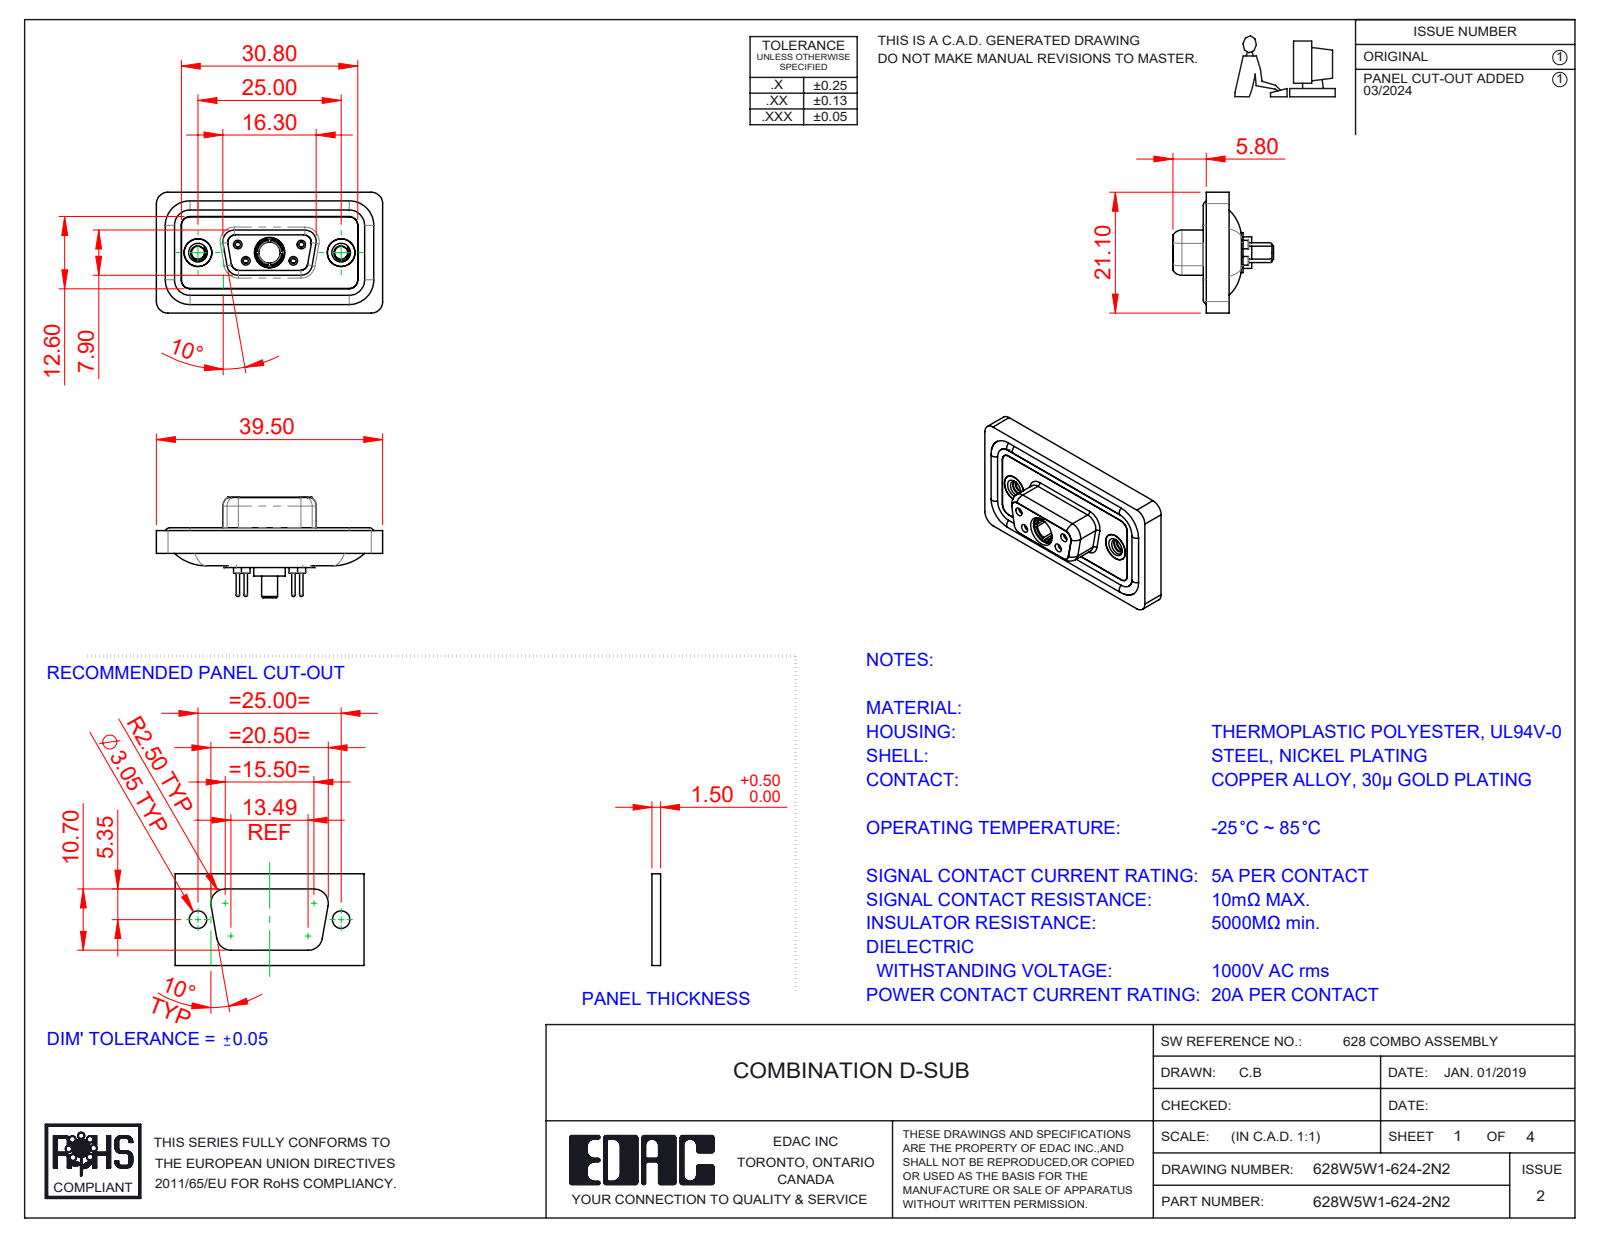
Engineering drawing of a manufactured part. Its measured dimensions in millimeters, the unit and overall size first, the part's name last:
Units: millimetres
Overall size (bounding box): 39.5 × 21.1 × 17.55
Round holes (diameter × count): ⌀0.9 ×4, ⌀1.1 ×4, ⌀1.5 ×4, ⌀2 ×4, ⌀4.85 ×3, ⌀1.6 ×2, ⌀1.7 ×2, ⌀2.26 ×2, ⌀4 ×2, ⌀4.05 ×2, ⌀5 ×2, ⌀3.7 ×1
Round bosses / shafts (diameter × count): ⌀1.6 ×6, ⌀2.2 ×4, ⌀0.6 ×4, ⌀4.95 ×2, ⌀4.8 ×2, ⌀5.5 ×1, ⌀5.2 ×1, ⌀4.96 ×1
Partial cylindrical surfaces — rounded edges, fillets, slot ends (radius × count): R1.5 ×22, R2 ×18, R1.35 ×8, R1.6 ×8, R0.25 ×4, R0.5 ×4, R0.6 ×4, R0.65 ×4
Main face-to-face distances: 0.4, 2.9, 1.1, 1.8, 1.6, 0.5, 5.65, 7.45, 5.35, 6.6
Hole centre spacings: 3.16, 5.72, 7.1, 12.5, 18.1, 4.39, 4.4, 8.31
Volume: 4 767 mm³ · Surface area: 7 635 mm²
Bodies: 13 solids, 680 faces (194 planar, 287 cylindrical, 199 other)
Part name (STEP PRODUCT): 628W5W1-624-2N2; 628Combo Shell Rear_09 Contacts; 628Combo Contact Row 1_24; 628Combo Shell Front_09 Contacts (+5 more)
STEP written by: SolidWorks 2023 (CONFIG_CONTROL_DESIGN)
